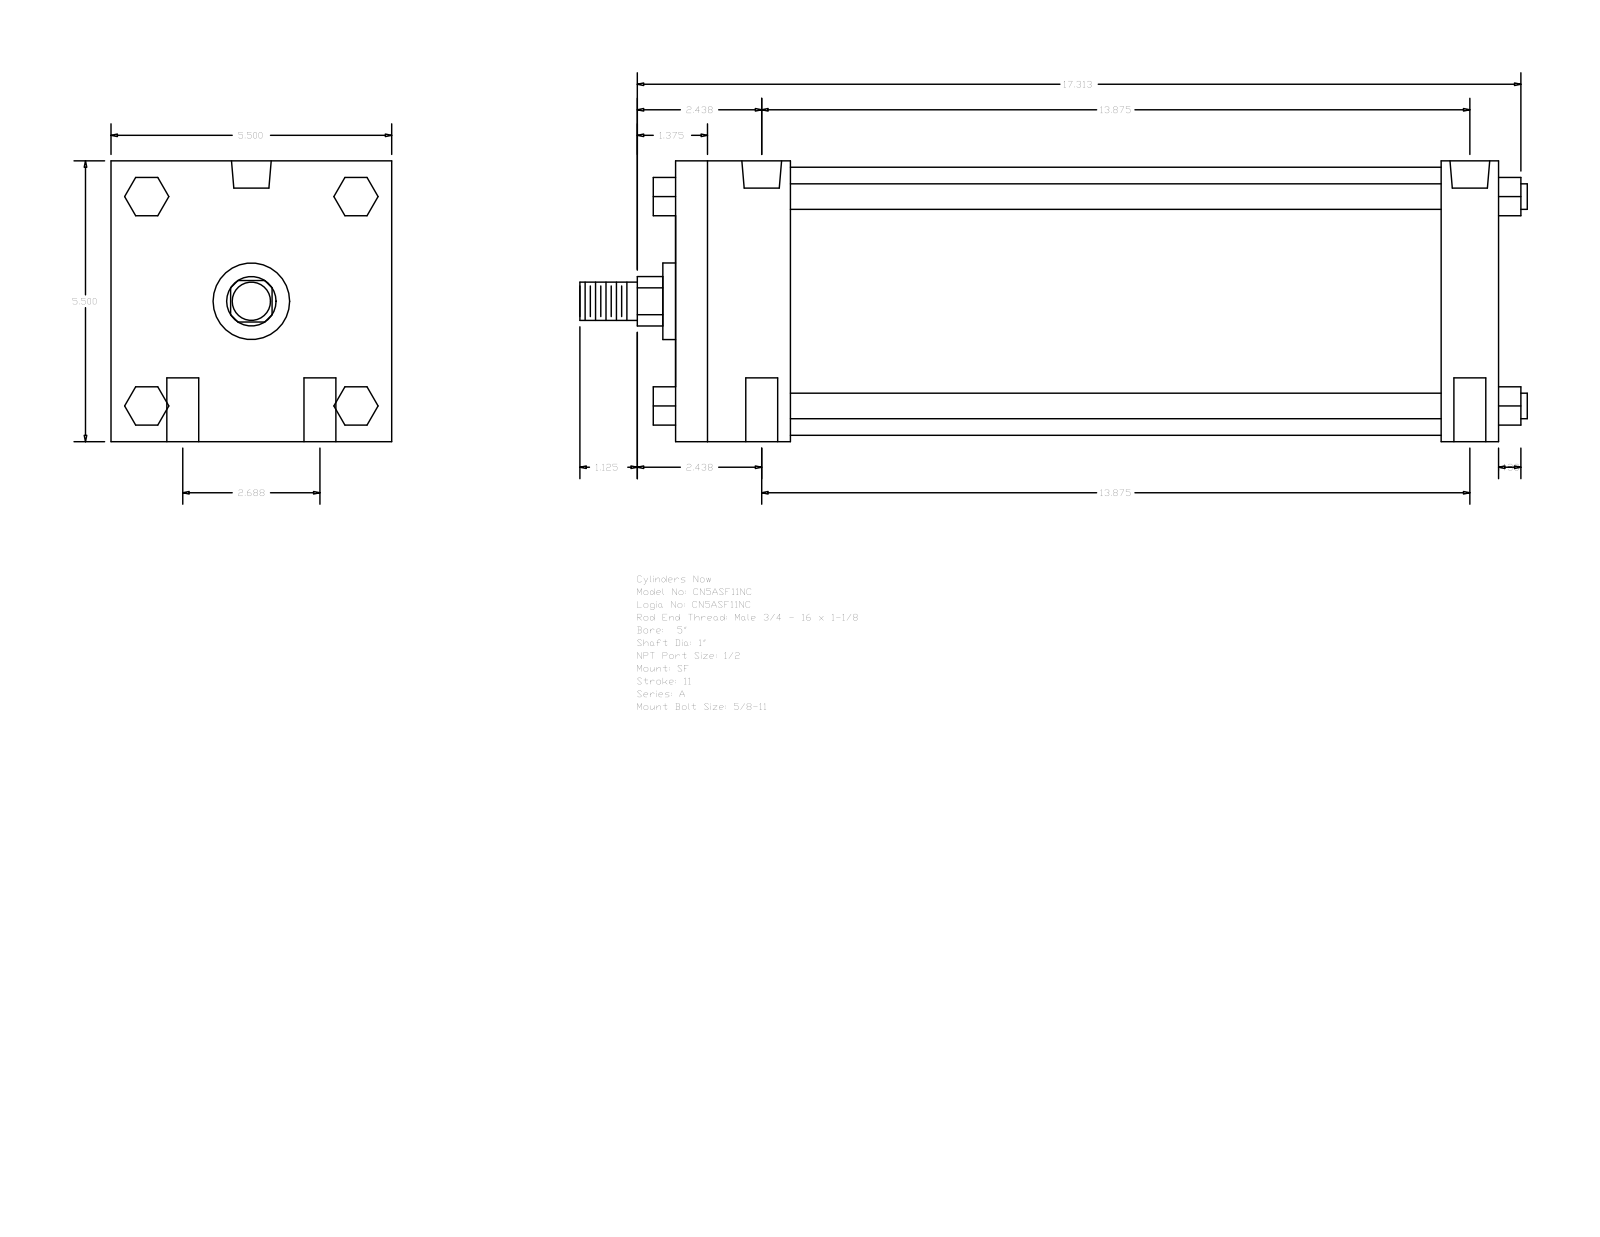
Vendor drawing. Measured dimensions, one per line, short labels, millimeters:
name: A_SF__0500_1
written by: GSSL Pune (CONFIG_CONTROL_DESIGN)
unit: mm
bodies: 0 solids, 124 faces (94 planar, 30 cylindrical, 0 other)
size: 471.49 × 139.7 × 139.7
holes: 4× ⌀15.88, 2× ⌀8.73, 2× ⌀19.77
bosses: 4× ⌀12.7, 1× ⌀133.35, 1× ⌀38.1, 1× ⌀25.4, 1× ⌀19.05
rounds: 1× R12.29
face distances: 139.7, 409.57, 28.57, 57.15, 381, 323.85, 352.42, 19.05, 52.07, 90.18
hole spacings: 34.13, 354.08, 352.43, 68.26, 358.98, 347.65
